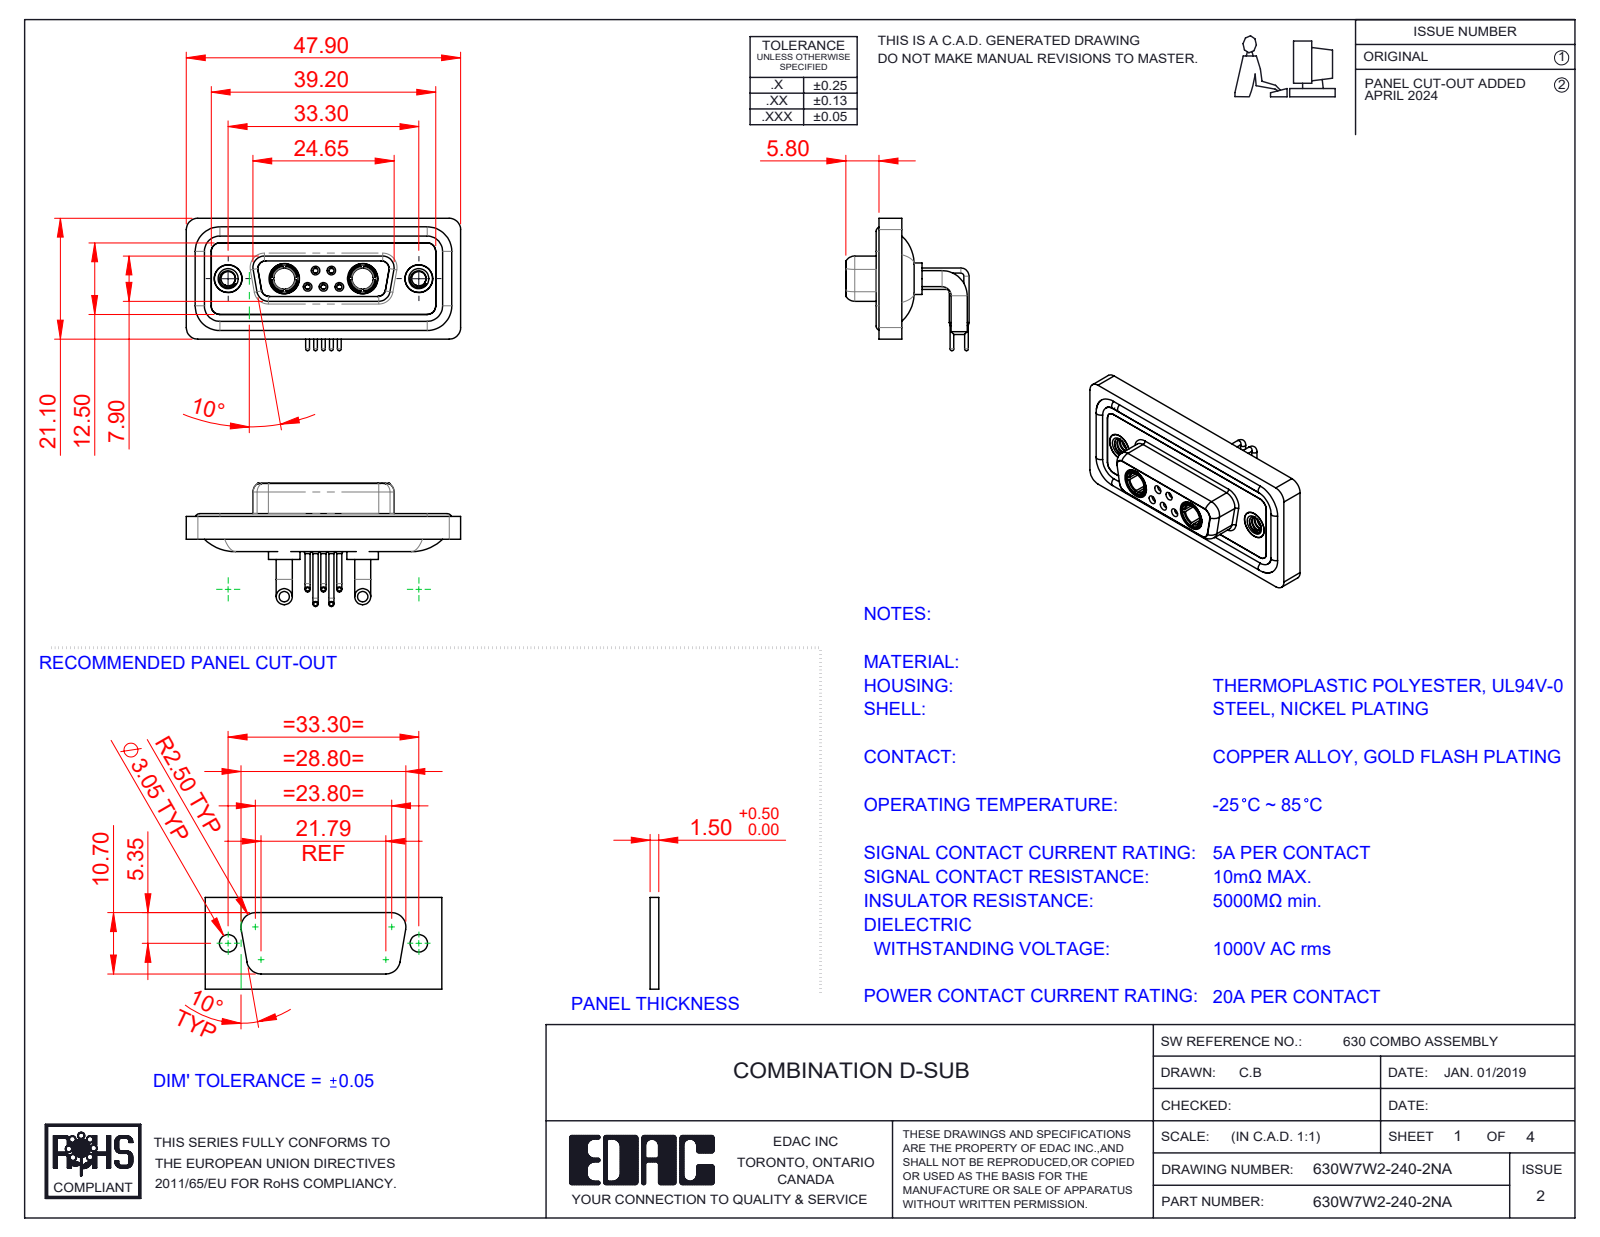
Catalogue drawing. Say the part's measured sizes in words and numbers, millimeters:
The part is named "630Combo Contact Row 2_50 Contacts; 630Combo Waterproof Housing_15 Contacts; 630Combo Threaded Rivet_A; 630Combo Housing_7W2 (+5 more)". Its 3-D file was written by "SolidWorks 2023 (CONFIG_CONTROL_DESIGN)". It is 16 solids with 801 faces: 238 planar, 351 cylindrical and 212 other. Overall it measures 47.9 by 23.12 by 21.53 millimeters. Its volume is 6 189 cubic millimeters and its surface area 10 209 square millimeters. Round holes: 5 of diameter 0.9, 5 of diameter 1.1, 5 of diameter 1.5, 5 of diameter 2, 4 of diameter 4.85, 3 of diameter 1.6, 2 of diameter 1.7, 2 of diameter 2.5, 2 of diameter 3.7, 2 of diameter 4, 2 of diameter 4.05, 2 of diameter 5. Round bosses or shafts: 6 of diameter 1.6, 5 of diameter 0.9, 5 of diameter 0.65, 4 of diameter 2.8, 2 of diameter 5.5, 2 of diameter 5.2, 2 of diameter 4.96, 2 of diameter 4.95. Partial cylindrical surfaces (rounded edges, fillets, slot ends): 20 of radius 2, 18 of radius 1.5, 12 of radius 1.35, 8 of radius 1.6, 4 of radius 0.25, 4 of radius 0.5, 4 of radius 0.6, 4 of radius 0.65. The main face-to-face distances are 0.4, 1.8, 1.1, 1.6, 2.9, 2.5, 3.1, 3.7, 4.1, 1.5. The hole center spacings are 3.16, 2.77, 9.8, 23.5, 4.31, 4.33, 5.03, 5.04.
